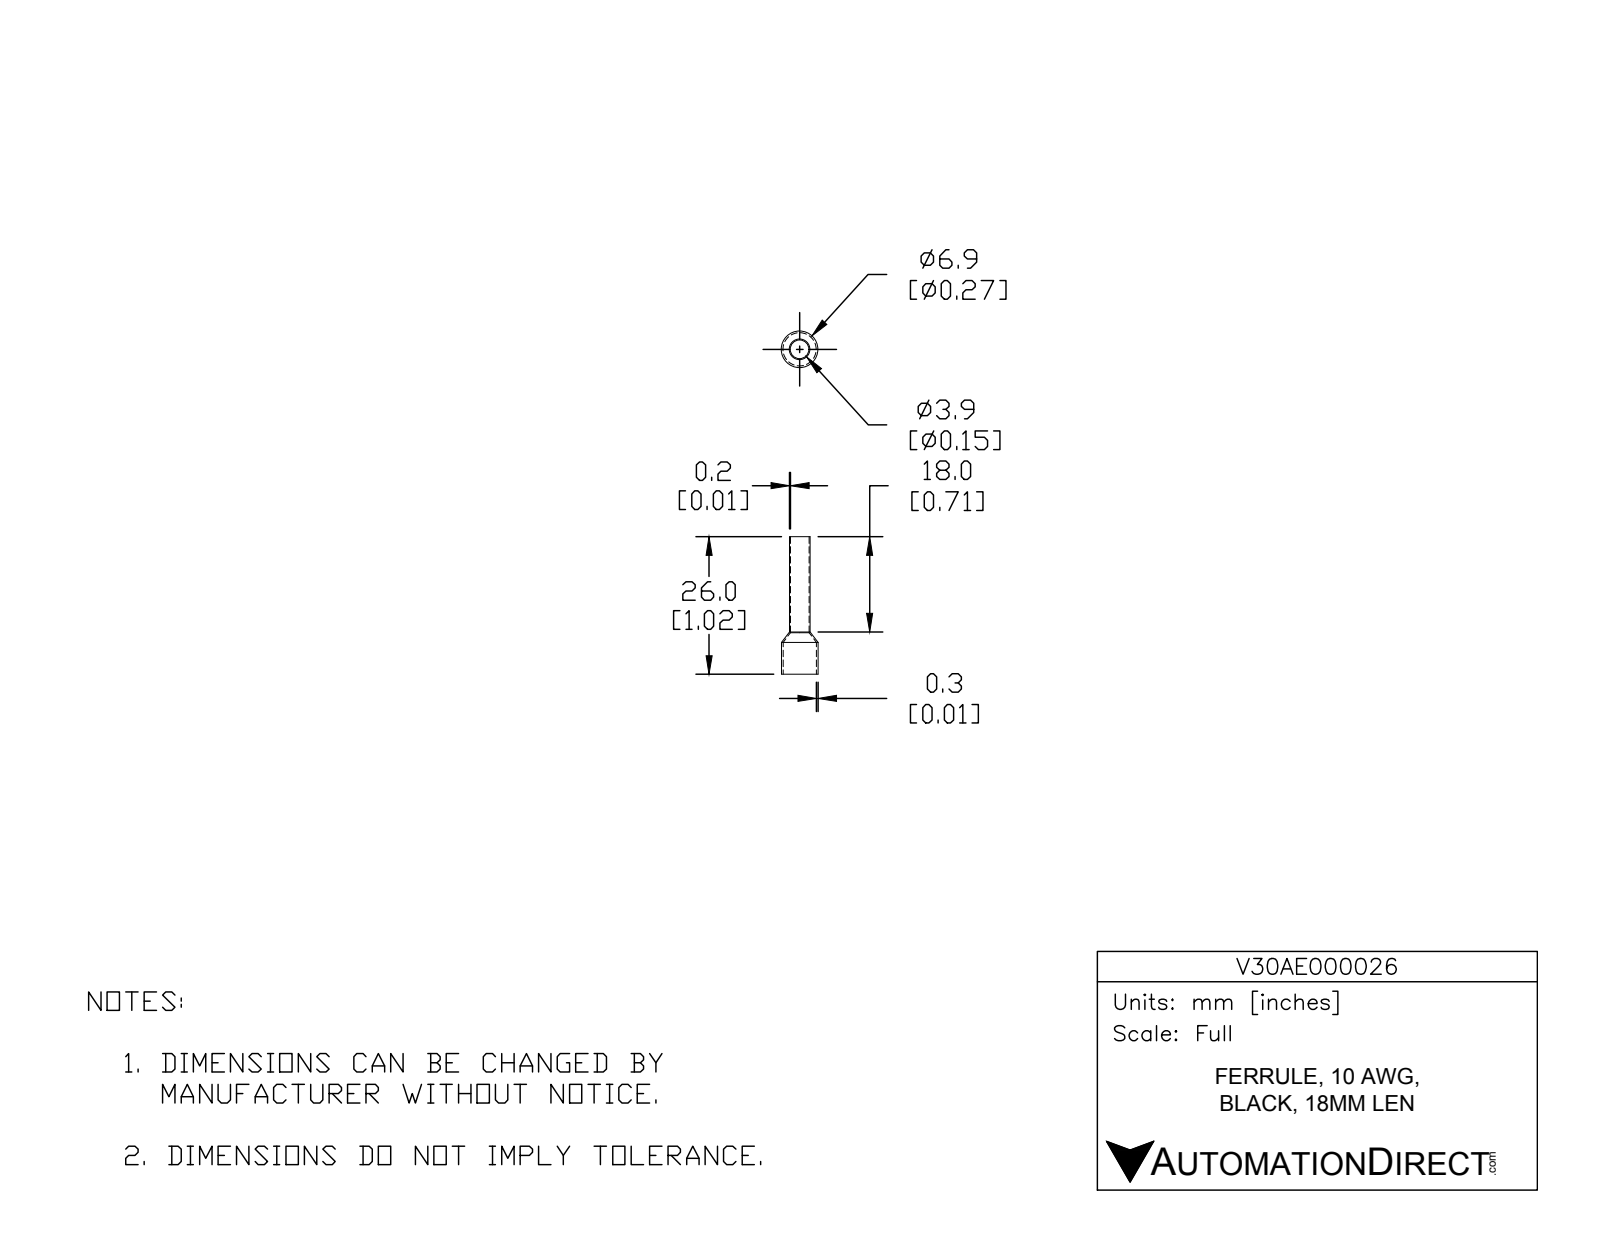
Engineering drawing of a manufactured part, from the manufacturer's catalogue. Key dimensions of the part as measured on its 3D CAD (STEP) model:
Part name (STEP PRODUCT): V30AE000026
STEP written by: SolidWorks 2017 (AUTOMOTIVE_DESIGN)
Units: millimetres
Bodies: 1 solid, 14 faces (2 planar, 8 cylindrical, 4 other)
Overall size (bounding box): 26 × 6.9 × 6.9
Volume: 89 mm³ · Surface area: 756 mm²
Round holes (diameter × count): ⌀3.5 ×1, ⌀6.3 ×1
Round bosses / shafts (diameter × count): ⌀6.9 ×1, ⌀3.9 ×1
Main face-to-face distances: 26
